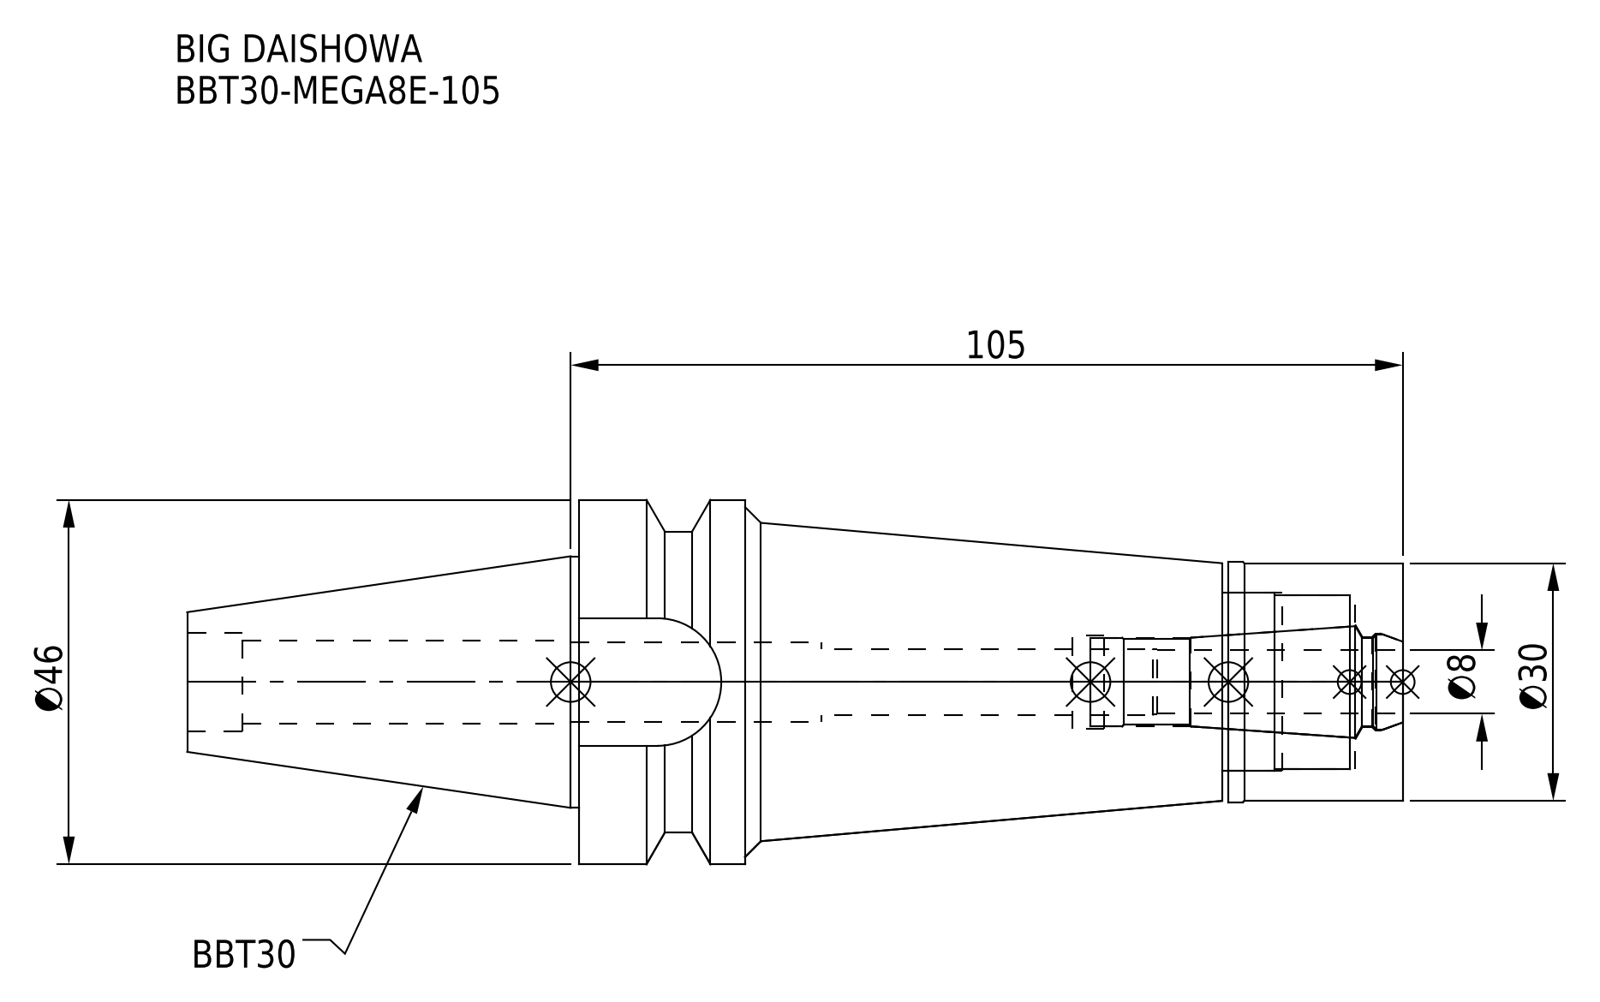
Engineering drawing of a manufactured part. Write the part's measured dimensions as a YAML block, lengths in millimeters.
part_name: "DXF_TEMP_ASSY_ASM_4_ASM.stp; BBT30-MEGA8E-105-080.stp; BBT30-MEGA8E-105_1.stp; BBT30ME08105-080_ASM.stp (+3 more)"
step_written_by: "SolidWorks 2019 (CONFIG_CONTROL_DESIGN)"
units: millimeters
bodies: {solids: 2, faces: 79, planar: 21, cylindrical: 38, other: 20}
overall_size: [153.4, 46, 46]
volume: 115639
surface_area: 26632
round_holes:
  - {diameter: 8.4, count: 1}
  - {diameter: 10, count: 1}
  - {diameter: 10.4, count: 1}
  - {diameter: 11.2, count: 1}
  - {diameter: 11.4, count: 1}
  - {diameter: 11.8, count: 1}
  - {diameter: 12.3, count: 1}
  - {diameter: 12.5, count: 1}
  - {diameter: 22, count: 1}
  - {diameter: 22.5, count: 1}
round_bosses_or_shafts:
  - {diameter: 46, count: 1}
  - {diameter: 31.75, count: 1}
  - {diameter: 30.3, count: 1}
  - {diameter: 30, count: 1}
partial_cylinders:
  - {radius: 8.05, count: 1}
  - {radius: 19, count: 1}
face_to_face_distances: [104, 22, 16.1, 82, 22.8, 0.8, 81.2, 32.6, 6.7, 15.3]
